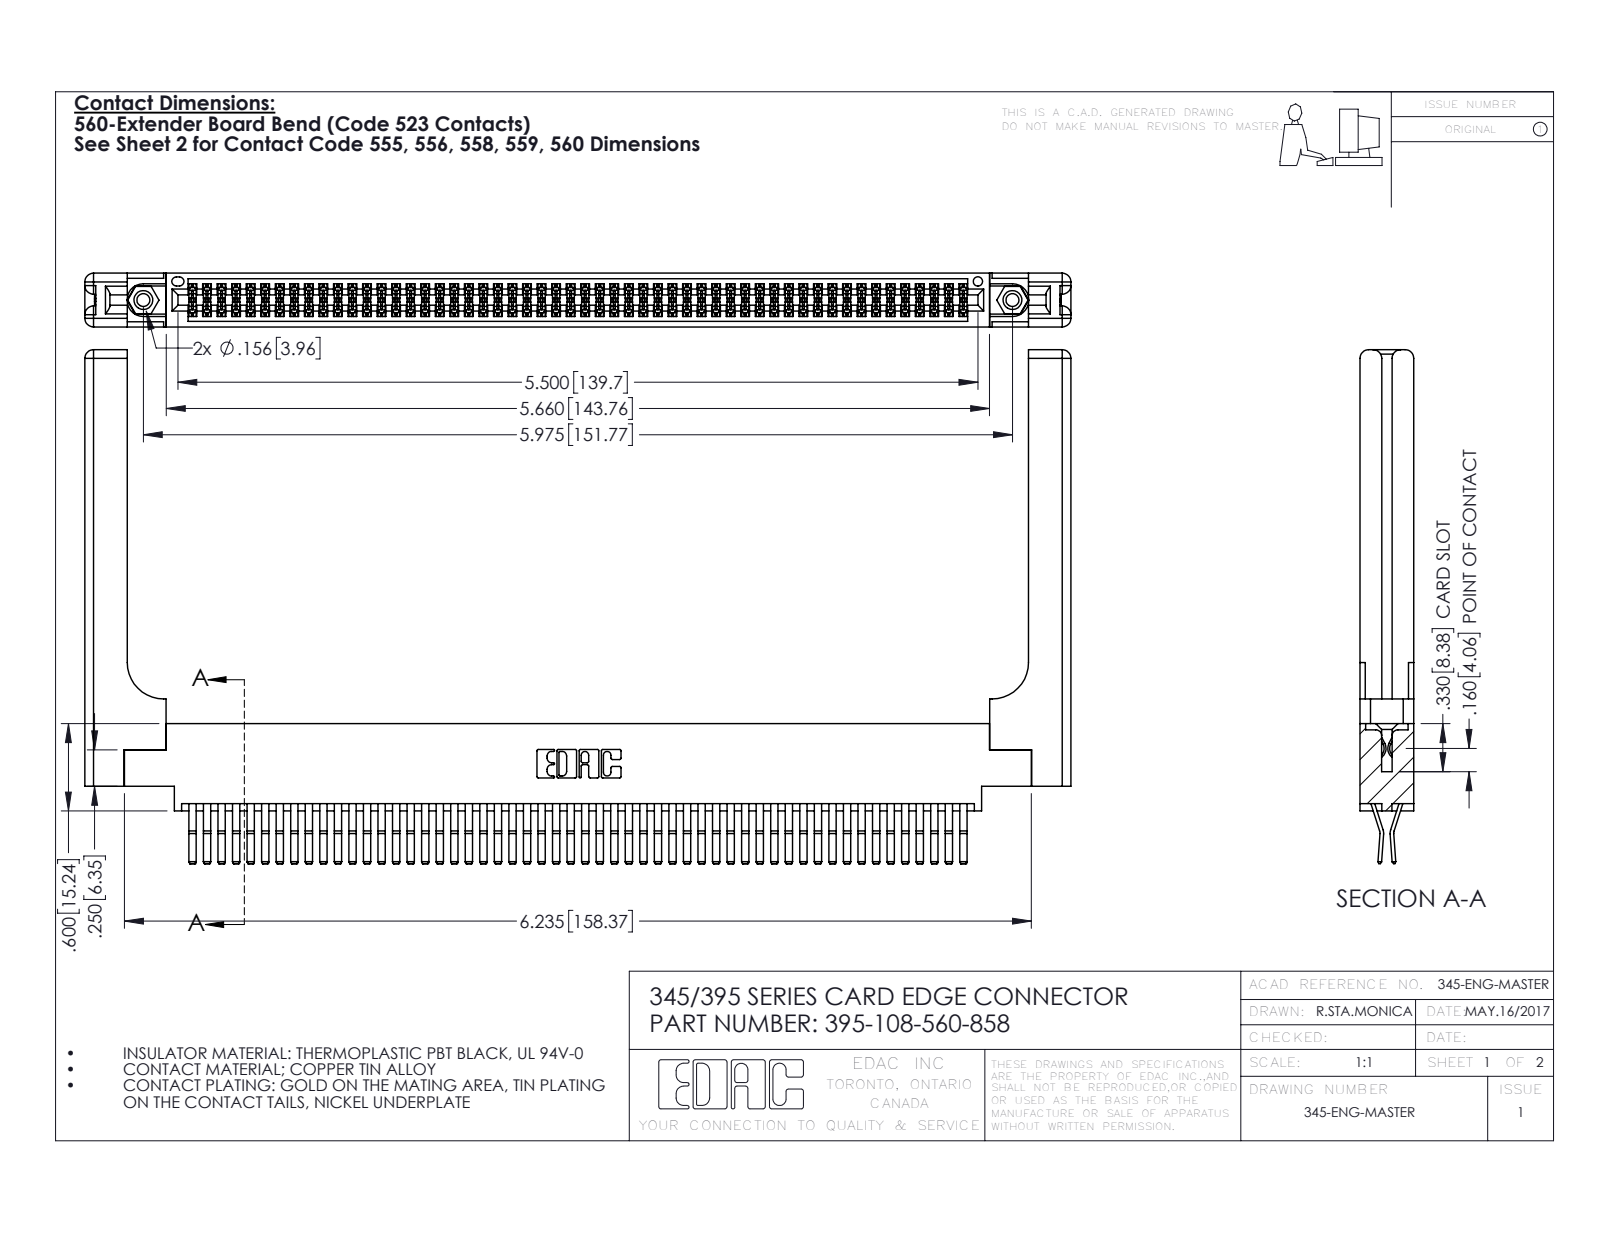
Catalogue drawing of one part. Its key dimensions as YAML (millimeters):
part_name: "345 Part_0.170 Offset - 0.156 Dia-TH; 395-108-560-858; 345-250-001_345-250-001-102; 345-292-001_560 Tail (+1 more)"
step_written_by: "SolidWorks 2016 (CONFIG_CONTROL_DESIGN)"
units: millimeters
bodies: {solids: 113, faces: 6002, planar: 3796, cylindrical: 2146, other: 60}
overall_size: [172.2, 89.7, 9.4]
volume: 25910
surface_area: 33030
round_holes:
  - {diameter: 2.3, count: 2}
  - {diameter: 3.2, count: 2}
  - {diameter: 4, count: 2}
  - {diameter: 1.6, count: 1}
round_bosses_or_shafts:
  - {diameter: 3.9, count: 2}
partial_cylinders:
  - {radius: 0.2, count: 162}
  - {radius: 0.3, count: 22}
  - {radius: 1.5, count: 16}
  - {radius: 0.2, count: 6}
  - {radius: 0.8, count: 6}
  - {radius: 0.7, count: 3}
  - {radius: 0.3, count: 2}
  - {radius: 0.4, count: 2}
face_to_face_distances: [1.8, 9.4, 7.6, 0.6, 2.5, 6.9, 5.1, 5.7, 4.4, 3.8]
hole_center_spacings: [6.9, 145.8, 151.8]
